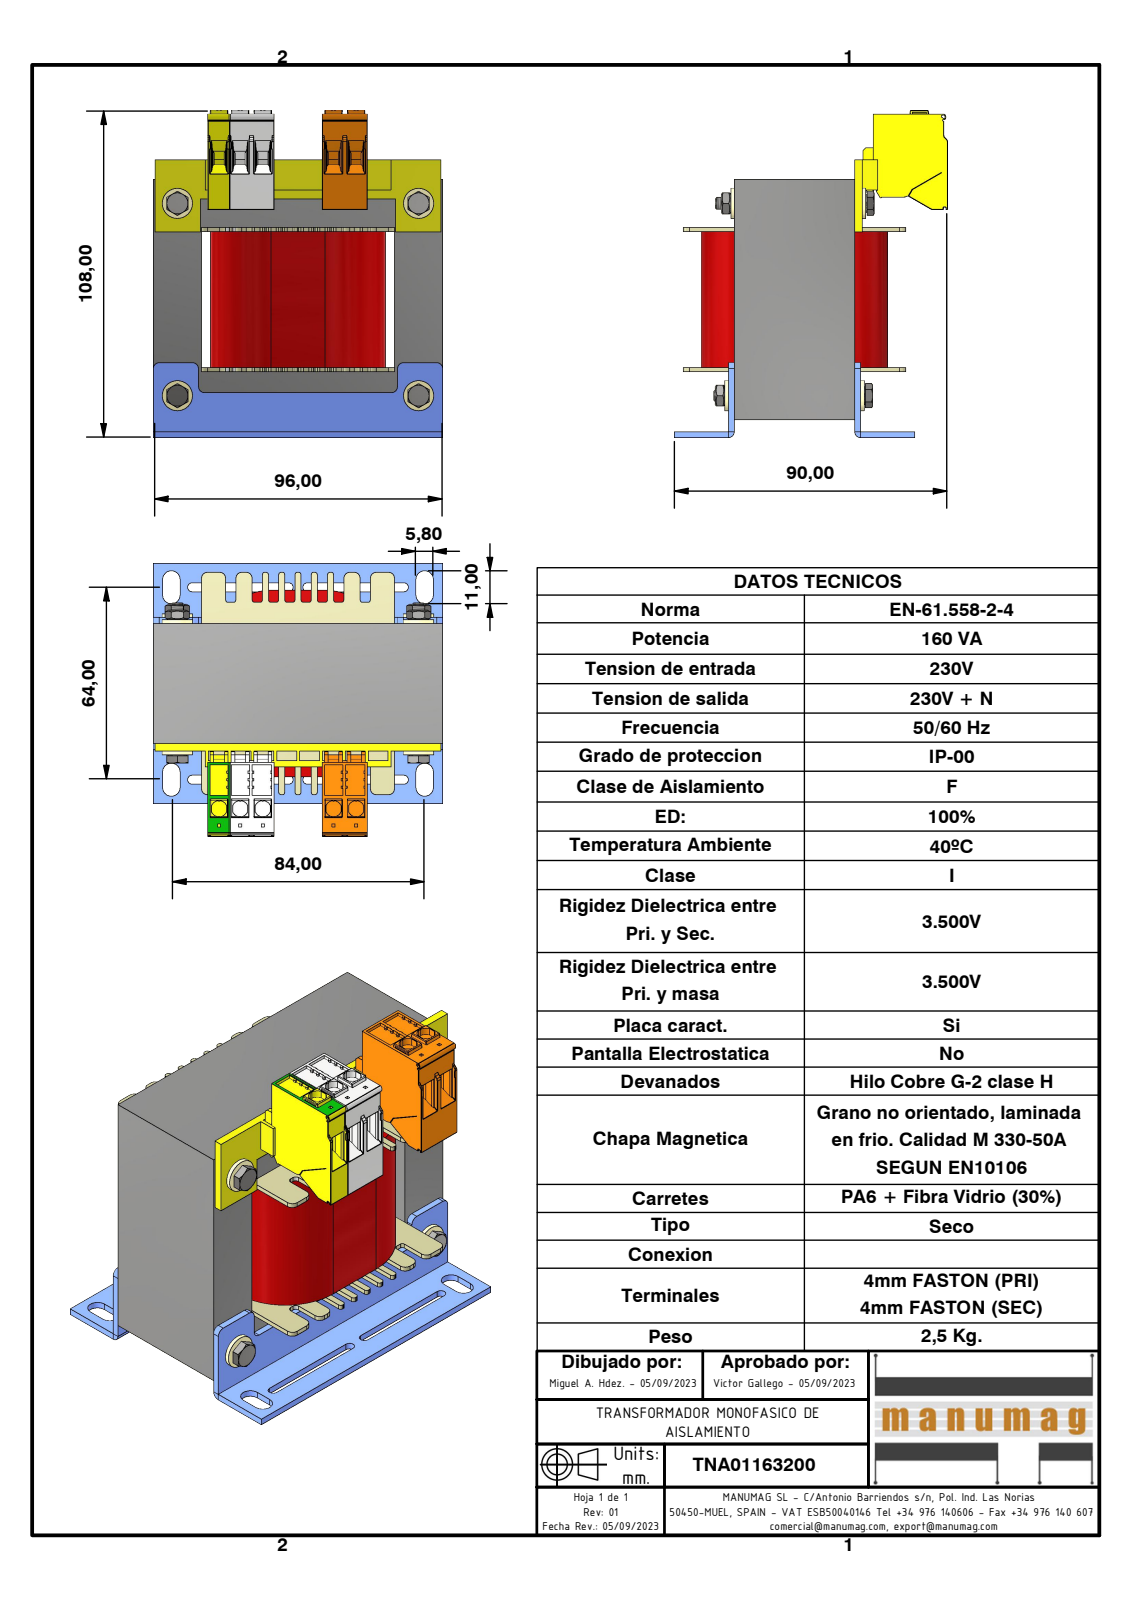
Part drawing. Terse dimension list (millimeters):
name: TNA01163200; EI96 x 80 - 40 (RC32); EI96; EI 96 X 80 - 40 (+7 more)
written by: Autodesk Inventor 2023 (AUTOMOTIVE_DESIGN)
unit: mm
bodies: 24 solids, 5325 faces (4333 planar, 688 cylindrical, 304 other)
size: 109 × 96 × 90.95
volume: 381 492 mm³; area: 107 700 mm²
holes: 4× ⌀3.24, 4× ⌀4, 4× ⌀5.5, 2× ⌀5.8
bosses: 4× ⌀10, 4× ⌀5.9, 4× ⌀4.9, 4× ⌀3.62
rounds: 214× R0.15, 58× R0.2, 51× R0.8, 22× R2, 14× R0.5, 8× R1.5, 8× R2.9, 6× R0.3
face distances: 64, 16, 32, 40, 48, 80, 2, 96, 22, 42
hole spacings: 64, 80, 102.45
